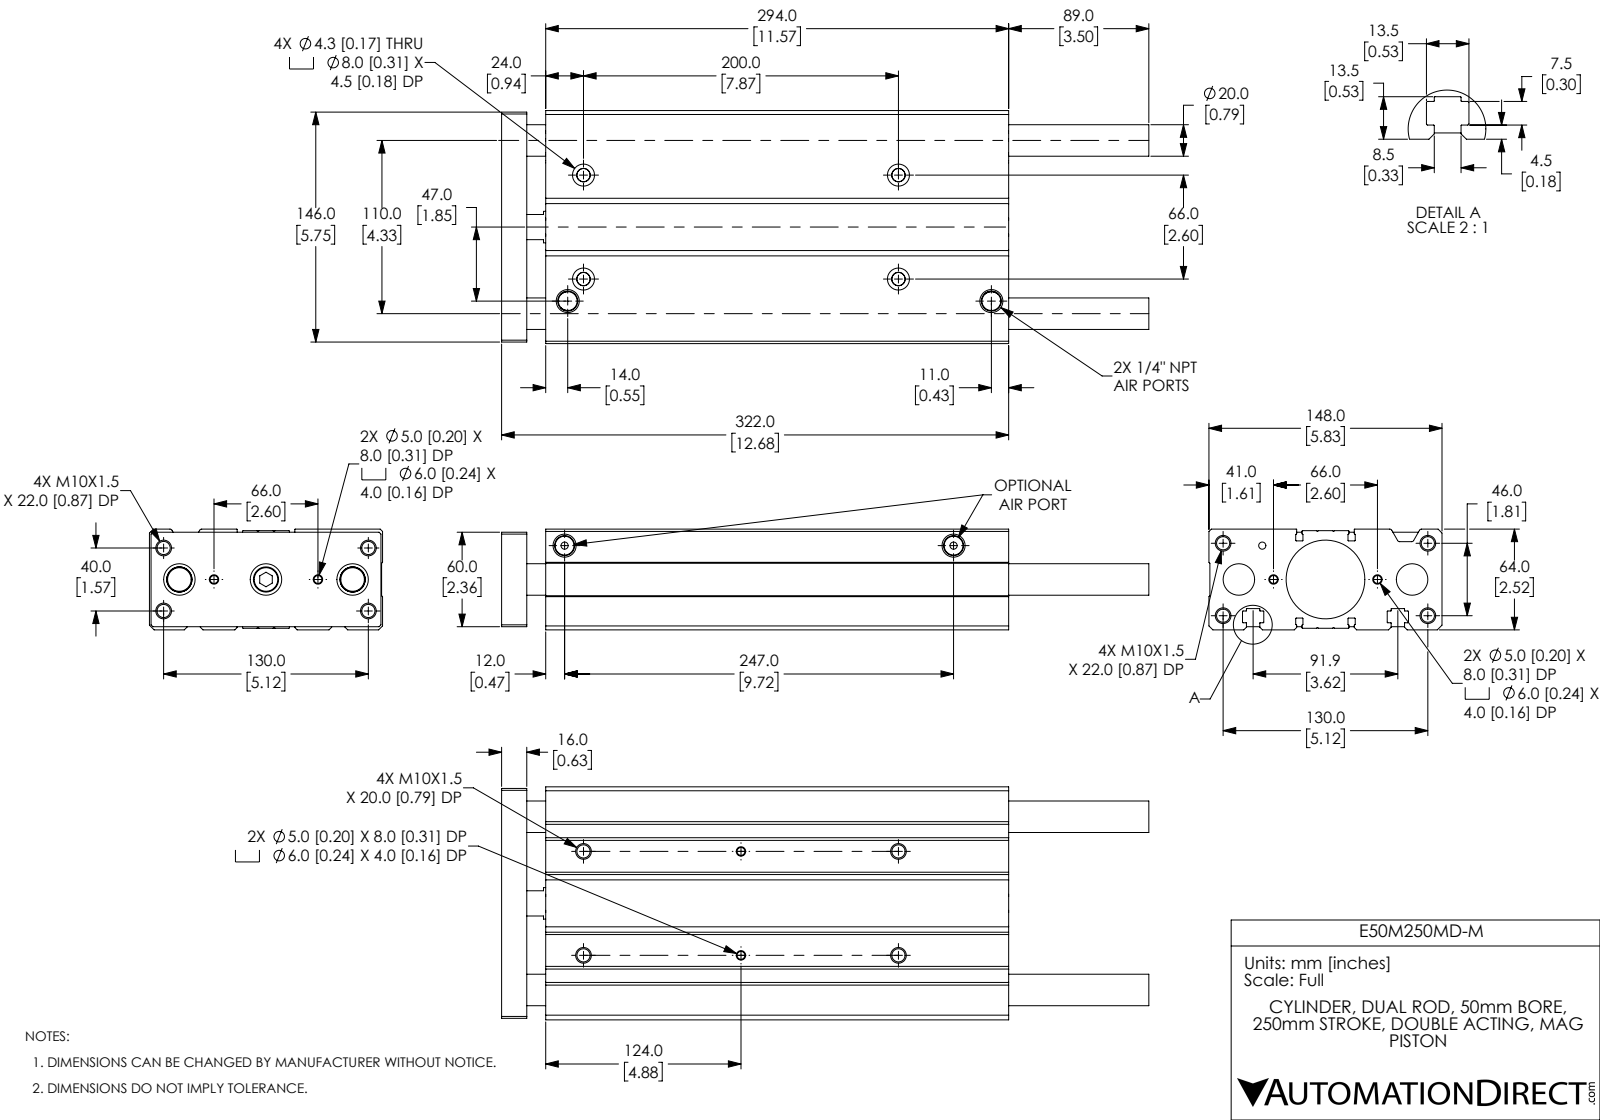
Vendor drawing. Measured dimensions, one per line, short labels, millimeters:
name: E50M250MD-M_ENDPLATE; E50M250MD-M; E50M250MD-M_BODY
written by: SolidWorks 2019 (CONFIG_CONTROL_DESIGN)
unit: mm
bodies: 5 solids, 423 faces (139 planar, 190 cylindrical, 94 other)
size: 411 × 148 × 64
volume: 2 353 000 mm³; area: 385 136 mm²
holes: 12× ⌀8.38, 4× ⌀5, 4× ⌀6, 4× ⌀8.6, 4× ⌀14, 3× ⌀4.57, 3× ⌀10, 3× ⌀20, 2× ⌀16, 1× ⌀20, 1× ⌀50, 1× ⌀50
bosses: 1× ⌀16
rounds: 32× R0.2, 28× R0.4, 4× R1.5, 2× R0.3
face distances: 64, 1, 63, 62, 148, 12, 0.6, 13.5, 5.5, 91.9
hole spacings: 3, 22.36, 25.08, 37.74, 39.41, 43, 66, 68.01
